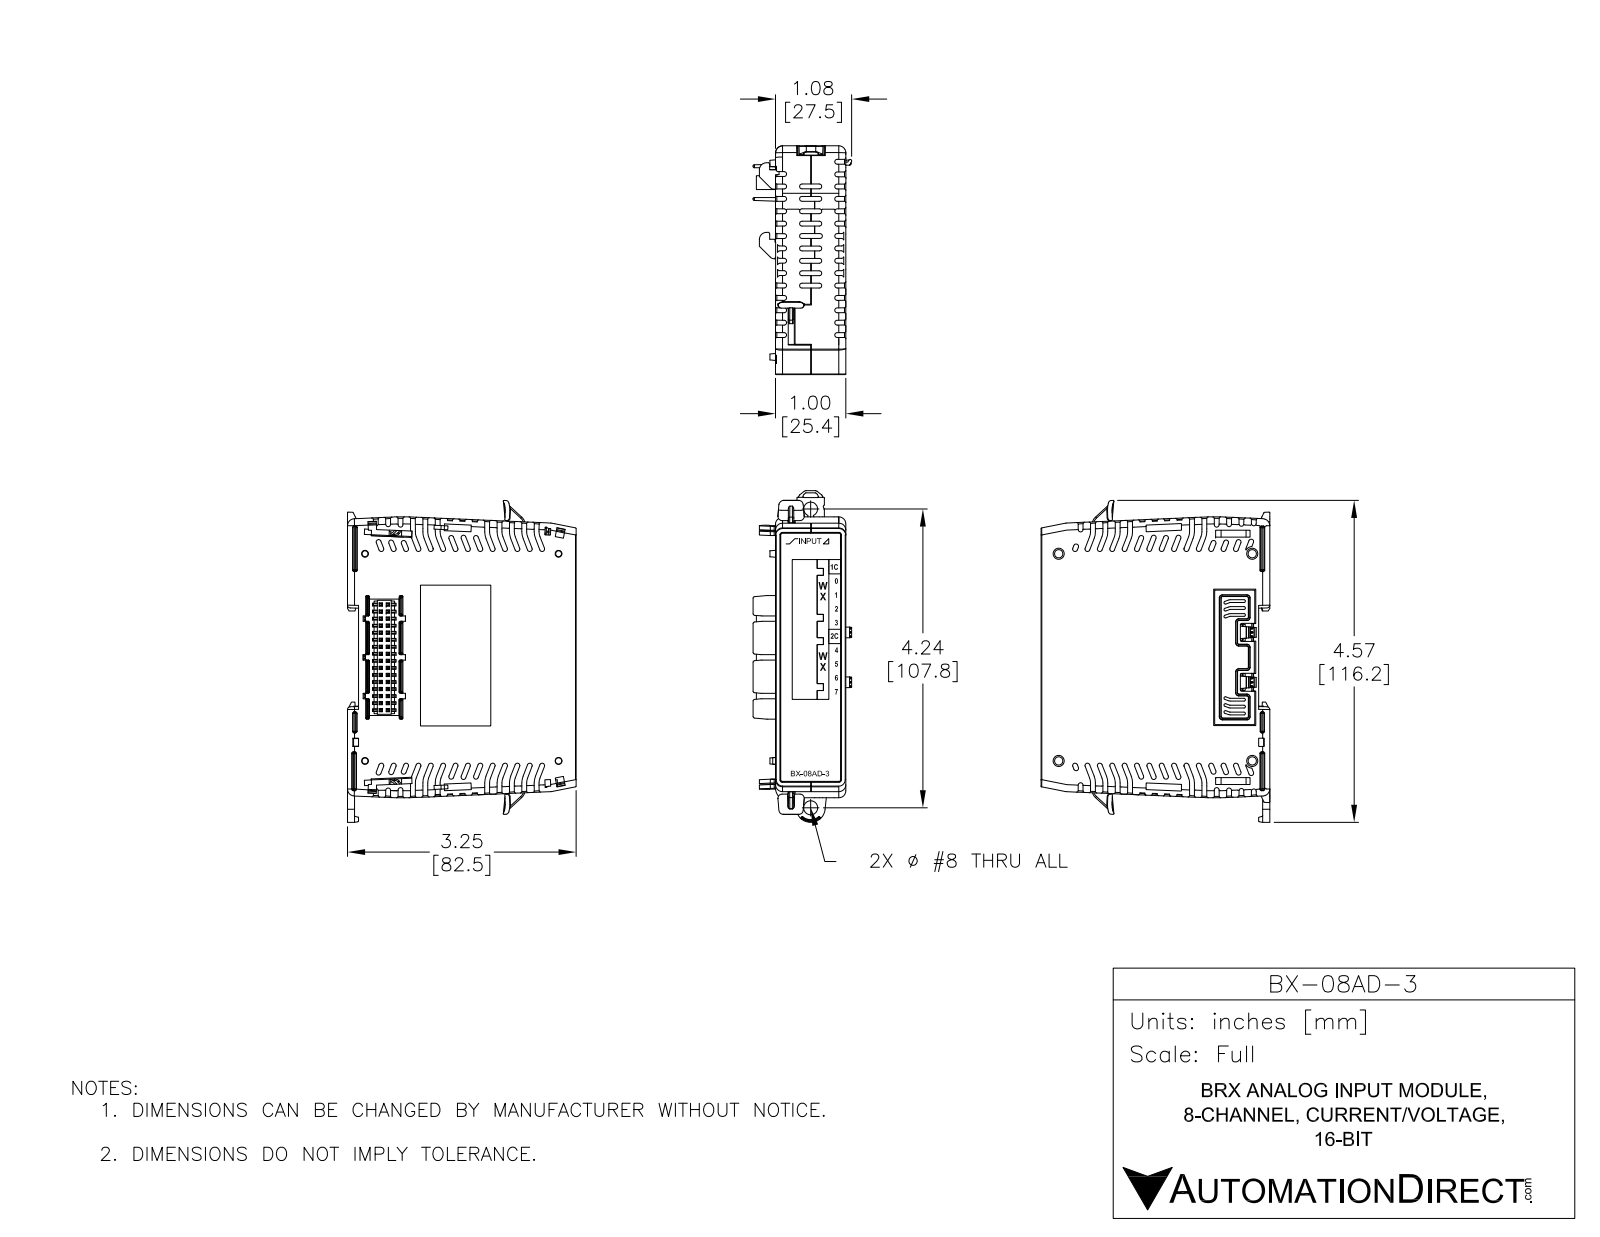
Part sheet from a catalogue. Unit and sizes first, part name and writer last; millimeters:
Units: millimetres
Overall size (bounding box): 116.5 × 82.55 × 35.62
Round holes (diameter × count): ⌀1.2 ×2, ⌀1.65 ×2, ⌀2.99 ×2, ⌀3 ×2, ⌀5.05 ×1
Round bosses / shafts (diameter × count): ⌀1.6 ×6, ⌀1.65 ×4, ⌀1.58 ×2, ⌀1.5 ×2
Partial cylindrical surfaces — rounded edges, fillets, slot ends (radius × count): R0.12 ×102, R0.25 ×47, R0.5 ×34, R0.12 ×24, R0.2 ×21, R2.98 ×14, R1 ×13, R0.25 ×12
Main face-to-face distances: 25.4, 81.55, 81.8, 12.06, 4, 77.55, 77.8, 2.54, 20, 16
Hole centre spacings: 2.54, 20.94, 23.34, 33.02, 53.17, 55.69, 65.67, 66.48
Volume: 189 656 mm³ · Surface area: 46 328 mm²
Bodies: 4 solids, 3616 faces (2545 planar, 583 cylindrical, 488 other)
Part name (STEP PRODUCT): Assem Clean Shell 2b NC w NEW1 BX08AD-3 Face3 With Faceplate A
STEP written by: SolidWorks 2021 (AUTOMOTIVE_DESIGN)
